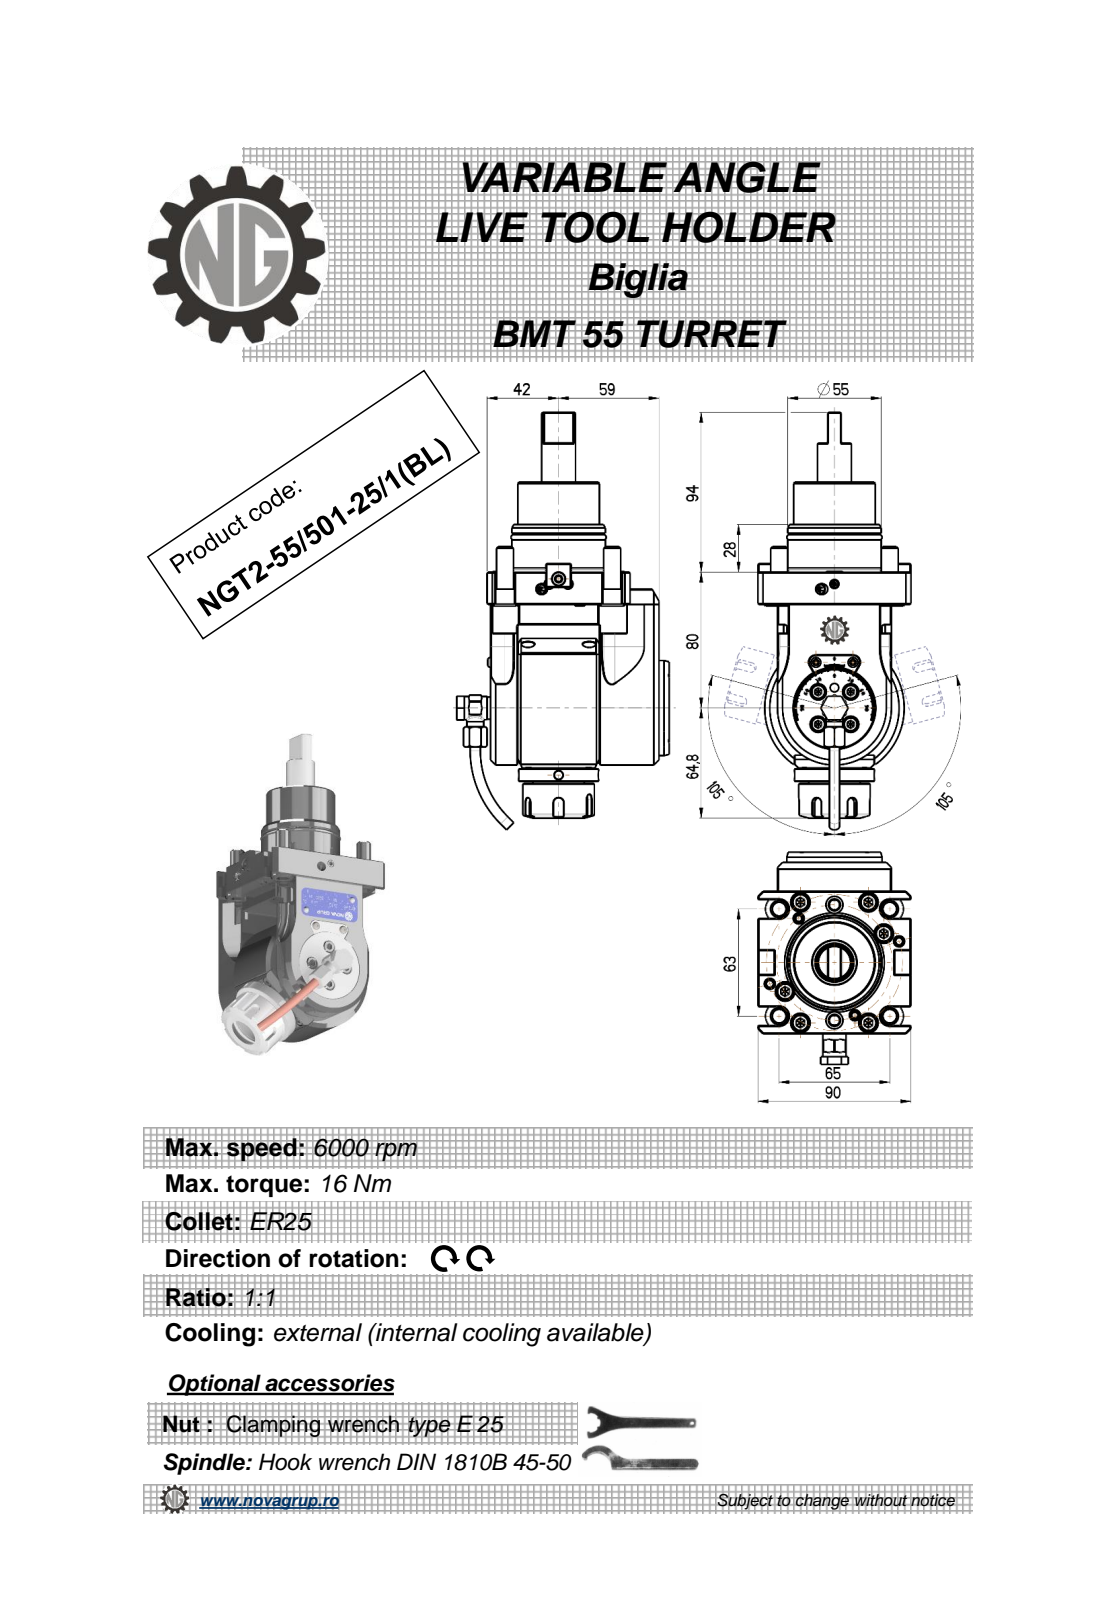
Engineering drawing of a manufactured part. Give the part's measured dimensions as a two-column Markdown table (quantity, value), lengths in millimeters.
| quantity | value |
| --- | --- |
| part name | NGT2_55_501_25_1_BL |
| STEP written by | PRO/ENGINEER BY PARAMETRIC TECHNOLOGY CORPORATION, 2010280 (CONFIG_CONTROL_DESIGN) |
| units | millimeters |
| bodies | 2 solids, 683 faces (295 planar, 178 cylindrical, 210 other) |
| overall size | 245.67 × 124.9 × 90 |
| volume | 894 898 mm³ |
| surface area | 93 014 mm² |
| round holes (diameter × count) | 4 × 3, 5 × 2, 6 × 2, 3 × 1, 6.2 × 1, 9 × 1, 11 × 1, 20.3 × 1 |
| round bosses / shafts (diameter × count) | 10 × 6, 6 × 4, 5.7 × 2, 82 × 1, 56 × 1, 55 × 1, 54.4 × 1, 50 × 1 |
| partial cylindrical surfaces (radius × count) | 0.32 × 20, 5 × 8, 8.5 × 8, 3 × 5, 0.5 × 4, 5.5 × 4, 8 × 4, 0.8 × 2 |
| main face-to-face distances | 31, 66, 18, 99, 41, 16, 2, 6, 48, 84 |
| hole center spacings | 34, 0.4, 15, 15.4, 39.45, 49, 49.4, 68 |
